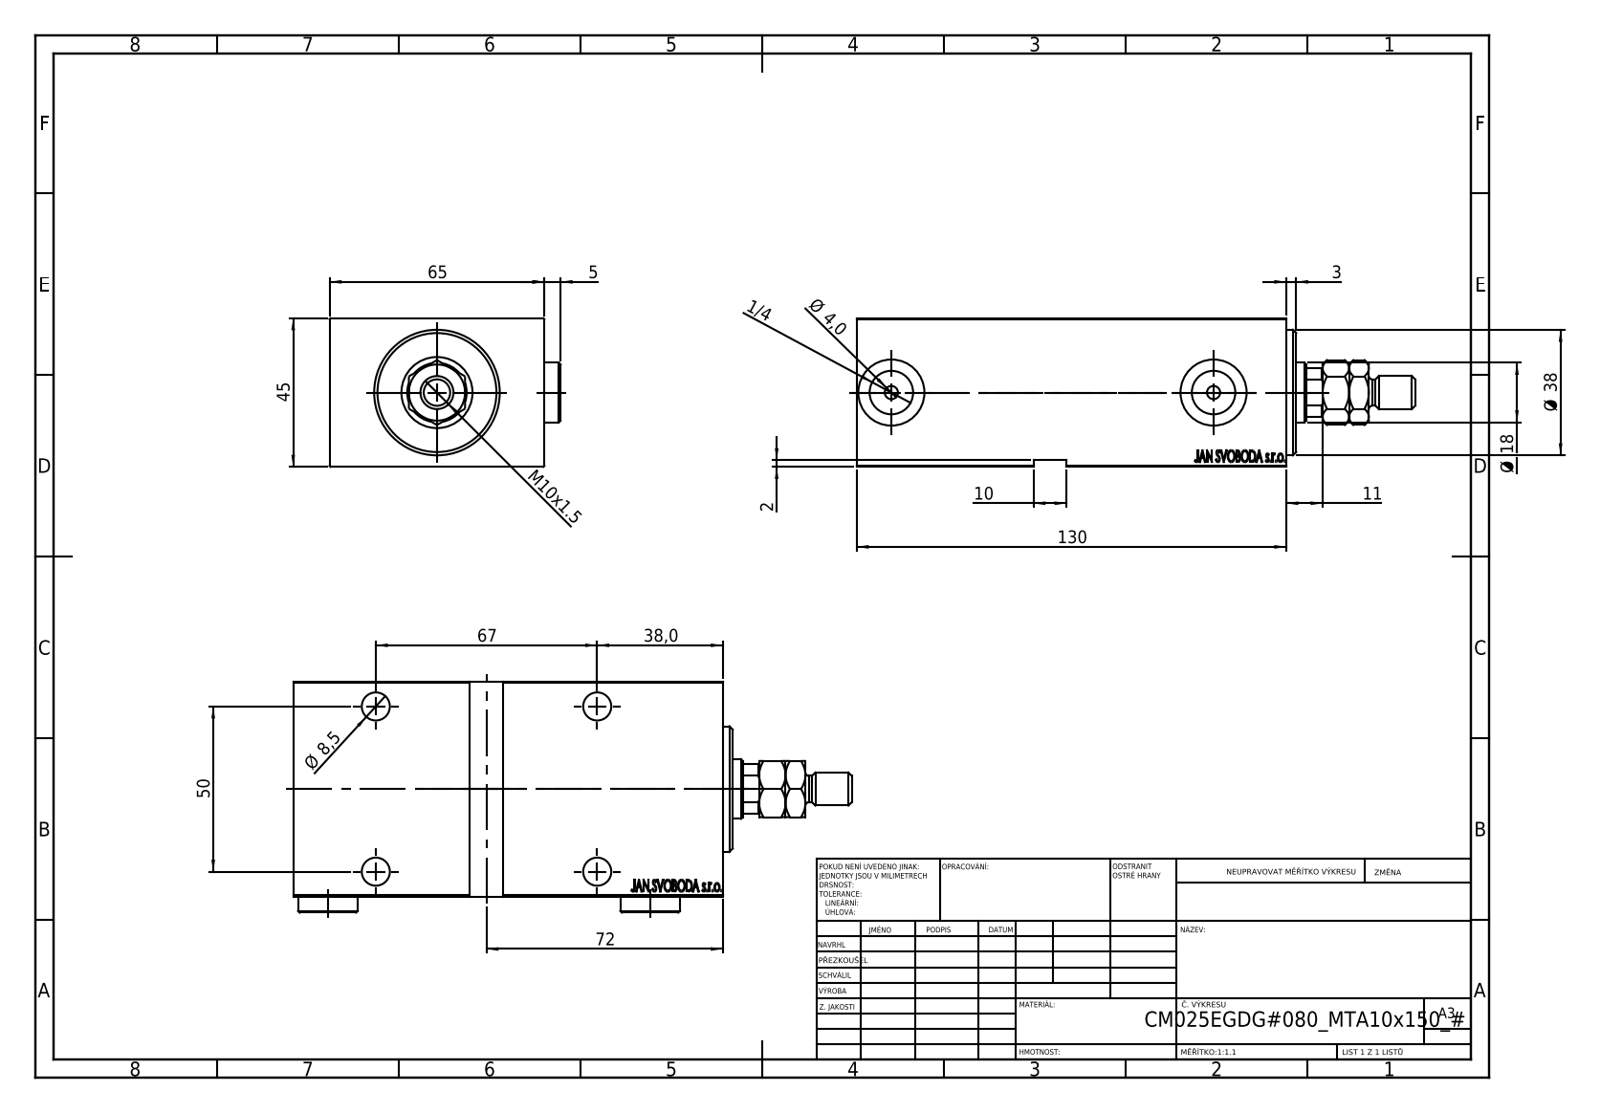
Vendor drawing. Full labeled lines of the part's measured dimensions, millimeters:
Part name (STEP PRODUCT): V450CM_E_VCP; Zatka_OIL_PORT; MTA; V450CM_E_Body (+1 more)
STEP written by: SolidWorks 2019 (CONFIG_CONTROL_DESIGN)
Units: millimetres
Bodies: 6 solids, 959 faces (459 planar, 72 cylindrical, 428 other)
Overall size (bounding box): 169 × 69.9 × 45
Volume: 351 178 mm³ · Surface area: 69 903 mm²
Round holes (diameter × count): ⌀8.5 ×5, ⌀13.5 ×4, ⌀4 ×2, ⌀13.16 ×2, ⌀20 ×2, ⌀18 ×1, ⌀21.5 ×1, ⌀25 ×1, ⌀35 ×1
Round bosses / shafts (diameter × count): ⌀18 ×2, ⌀38 ×1, ⌀27 ×1, ⌀10 ×1, ⌀8 ×1
Partial cylindrical surfaces — rounded edges, fillets, slot ends (radius × count): R8.5 ×1
Main face-to-face distances: 45, 65, 130, 5, 64.9, 6, 8, 124, 125, 119
Hole centre spacings: 50, 67, 83.6, 97.5
